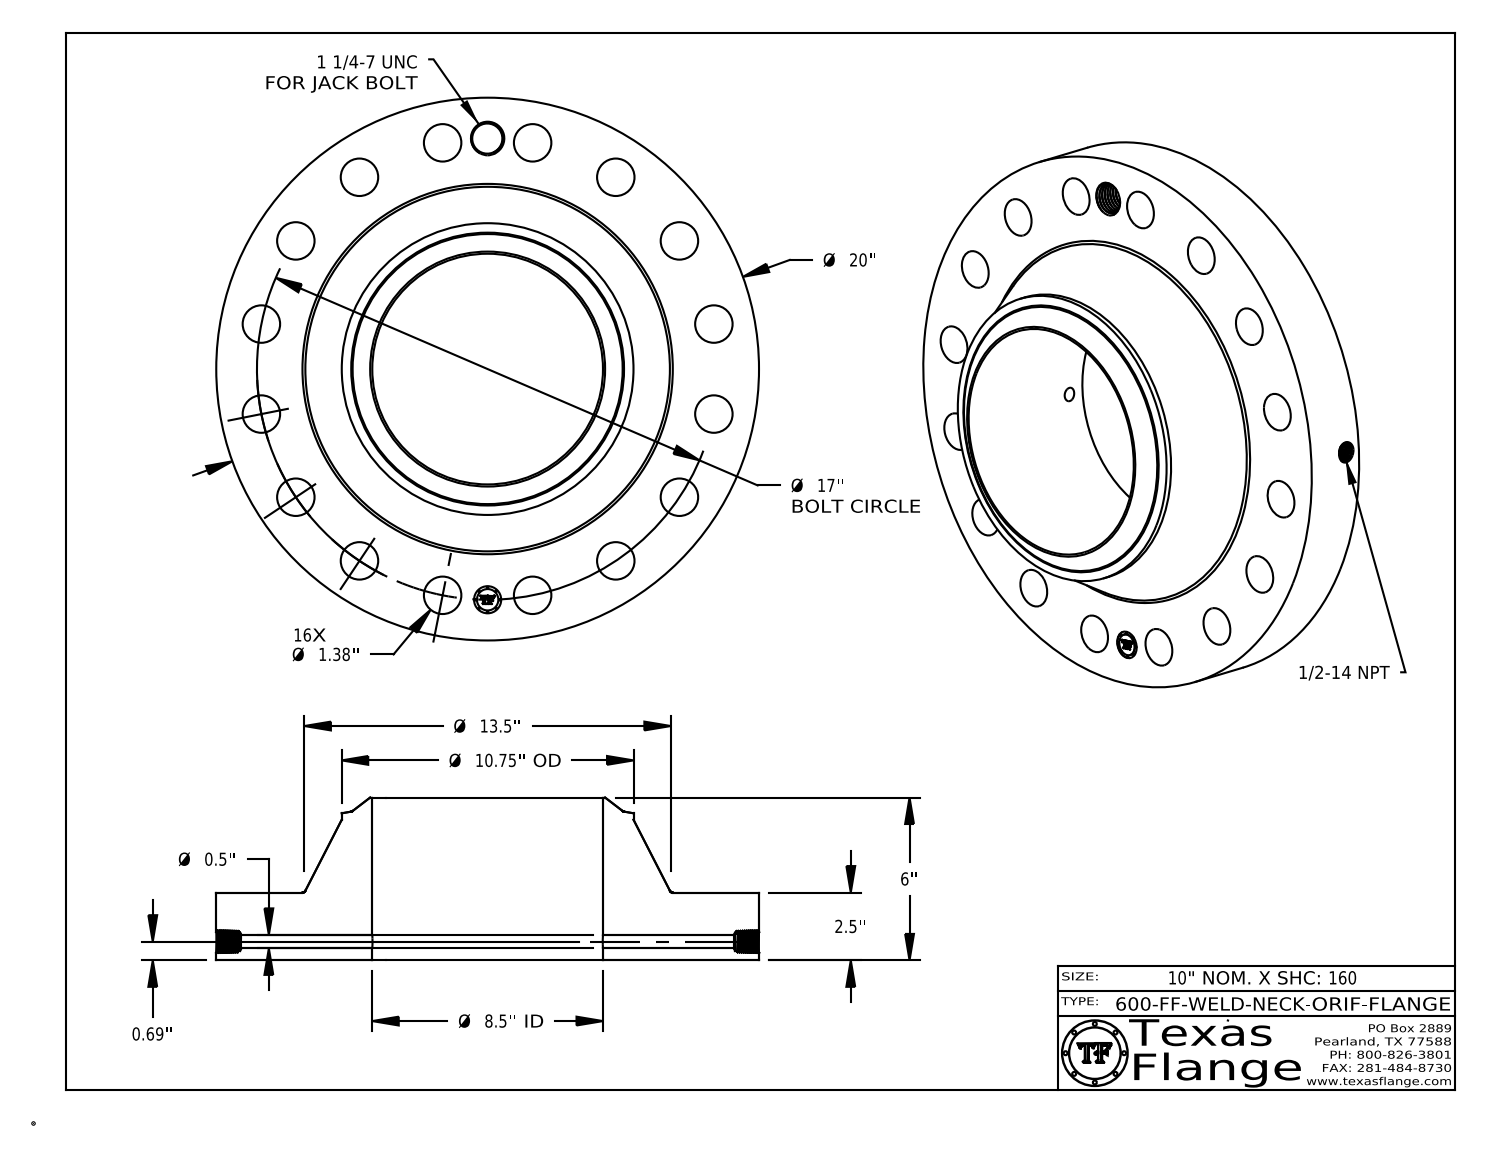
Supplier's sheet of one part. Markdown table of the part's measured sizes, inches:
| quantity | value |
| --- | --- |
| part name | 600-FF-WELD-NECK |
| STEP written by | CATIA V5 STEP AP214 (AUTOMOTIVE_DESIGN) |
| units | inches |
| bodies | 1 solid, 803 faces (368 planar, 113 cylindrical, 322 other) |
| overall size | 20 × 20 × 6 |
| volume | 753.2 in³ |
| surface area | 1 065 in² |
| round holes (diameter × count) | 1.38 × 16, 0.5 × 1, 0.672 × 1, 1 × 1, 1.109 × 1, 8.5 × 1 |
| round bosses / shafts (diameter × count) | 0.061 × 8, 20 × 1, 10.75 × 1, 0.788 × 1 |
| main face-to-face distances | 2.5, 6, 3.5, 2.485, 0.015, 3.515, 0.298, 0.293, 0.054, 0.248 |
| hole center spacings | 8.5, 12.021, 15.706, 16.673, 3.317, 9.444, 14.135, 17 |
